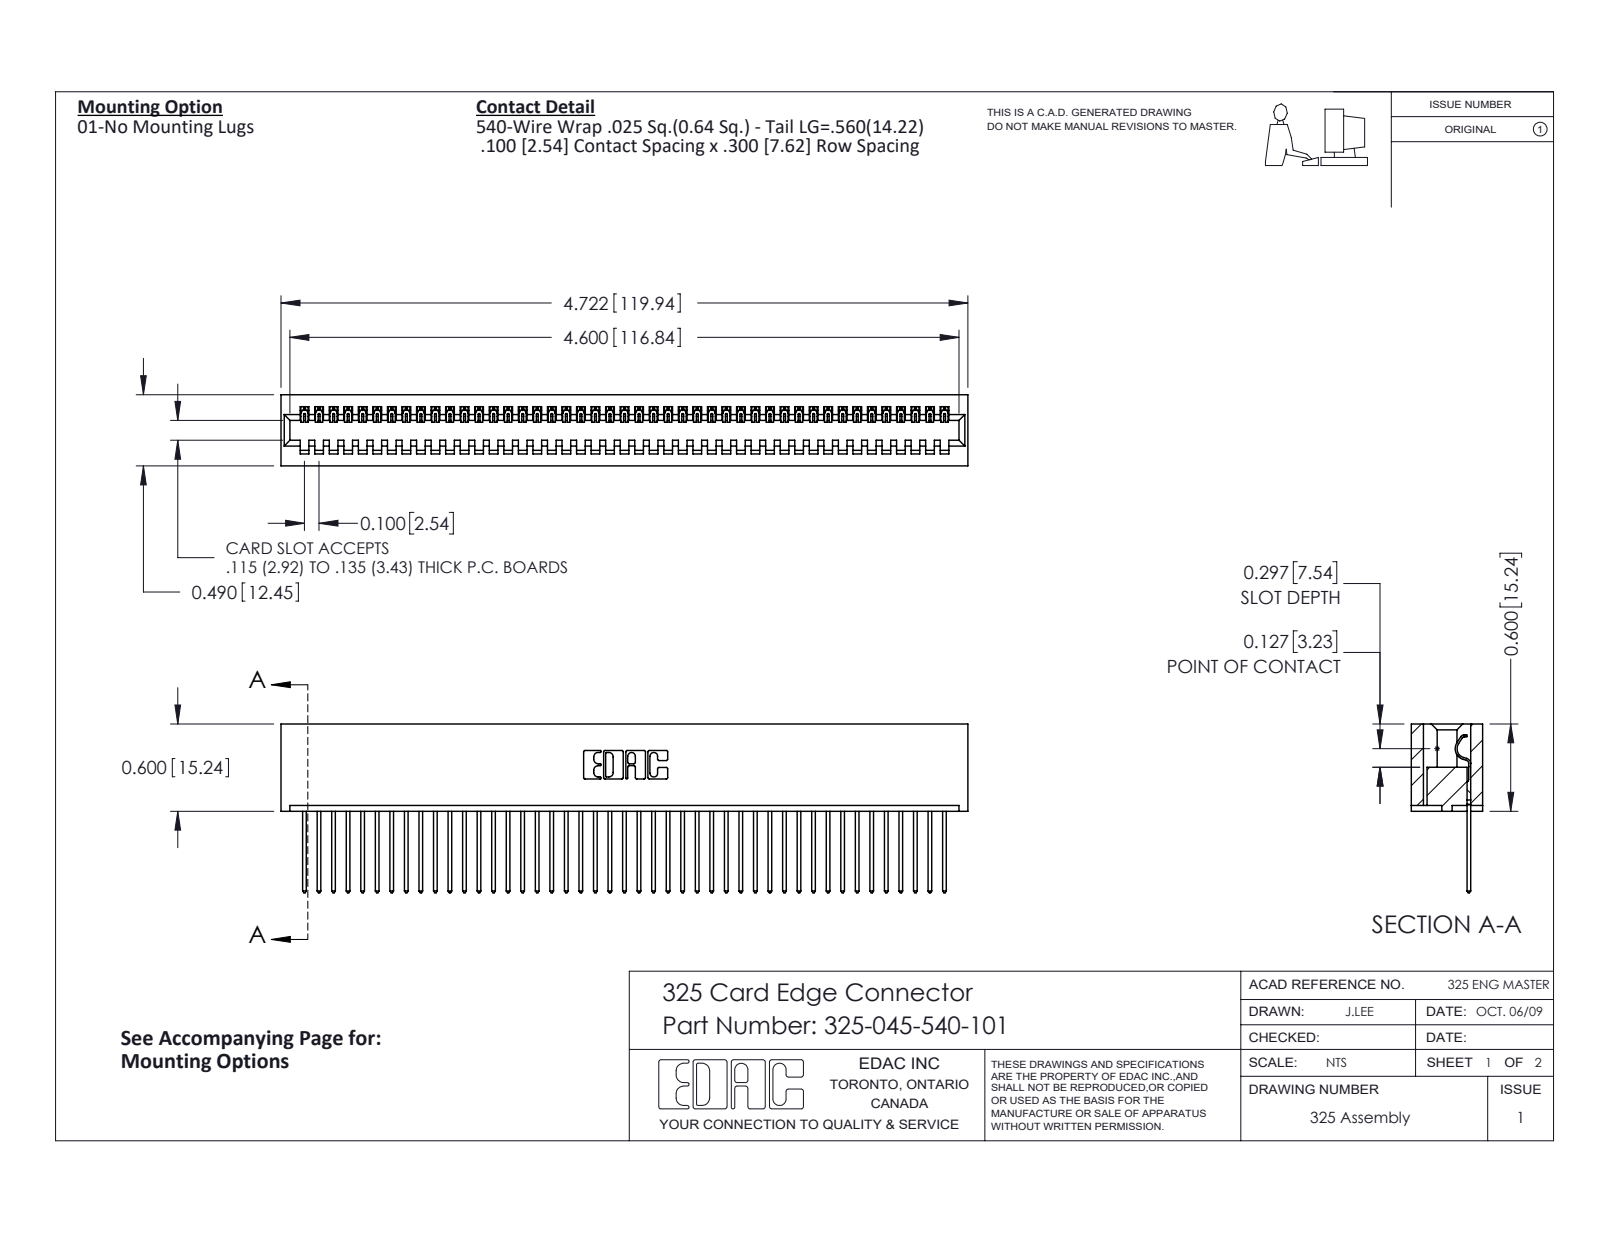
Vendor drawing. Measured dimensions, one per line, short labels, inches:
name: 325 Part_Lugless; 325-045-540-101; 325-292-001_325-293-140
written by: SolidWorks 2016 (CONFIG_CONTROL_DESIGN)
unit: in
bodies: 46 solids, 2716 faces (1956 planar, 760 cylindrical, 0 other)
size: 4.722 × 1.16 × 0.49
volume: 0.969 in³; area: 28.43 in²
rounds: 90× R0.006, 90× R0.01, 22× R0.01, 6× R0.007, 6× R0.031, 3× R0.026, 1× R0.014, 1× R0.022
face distances: 0.083, 0.407, 0.3, 0.49, 0.107, 0.383, 0.025, 0.325, 0.56, 0.263
